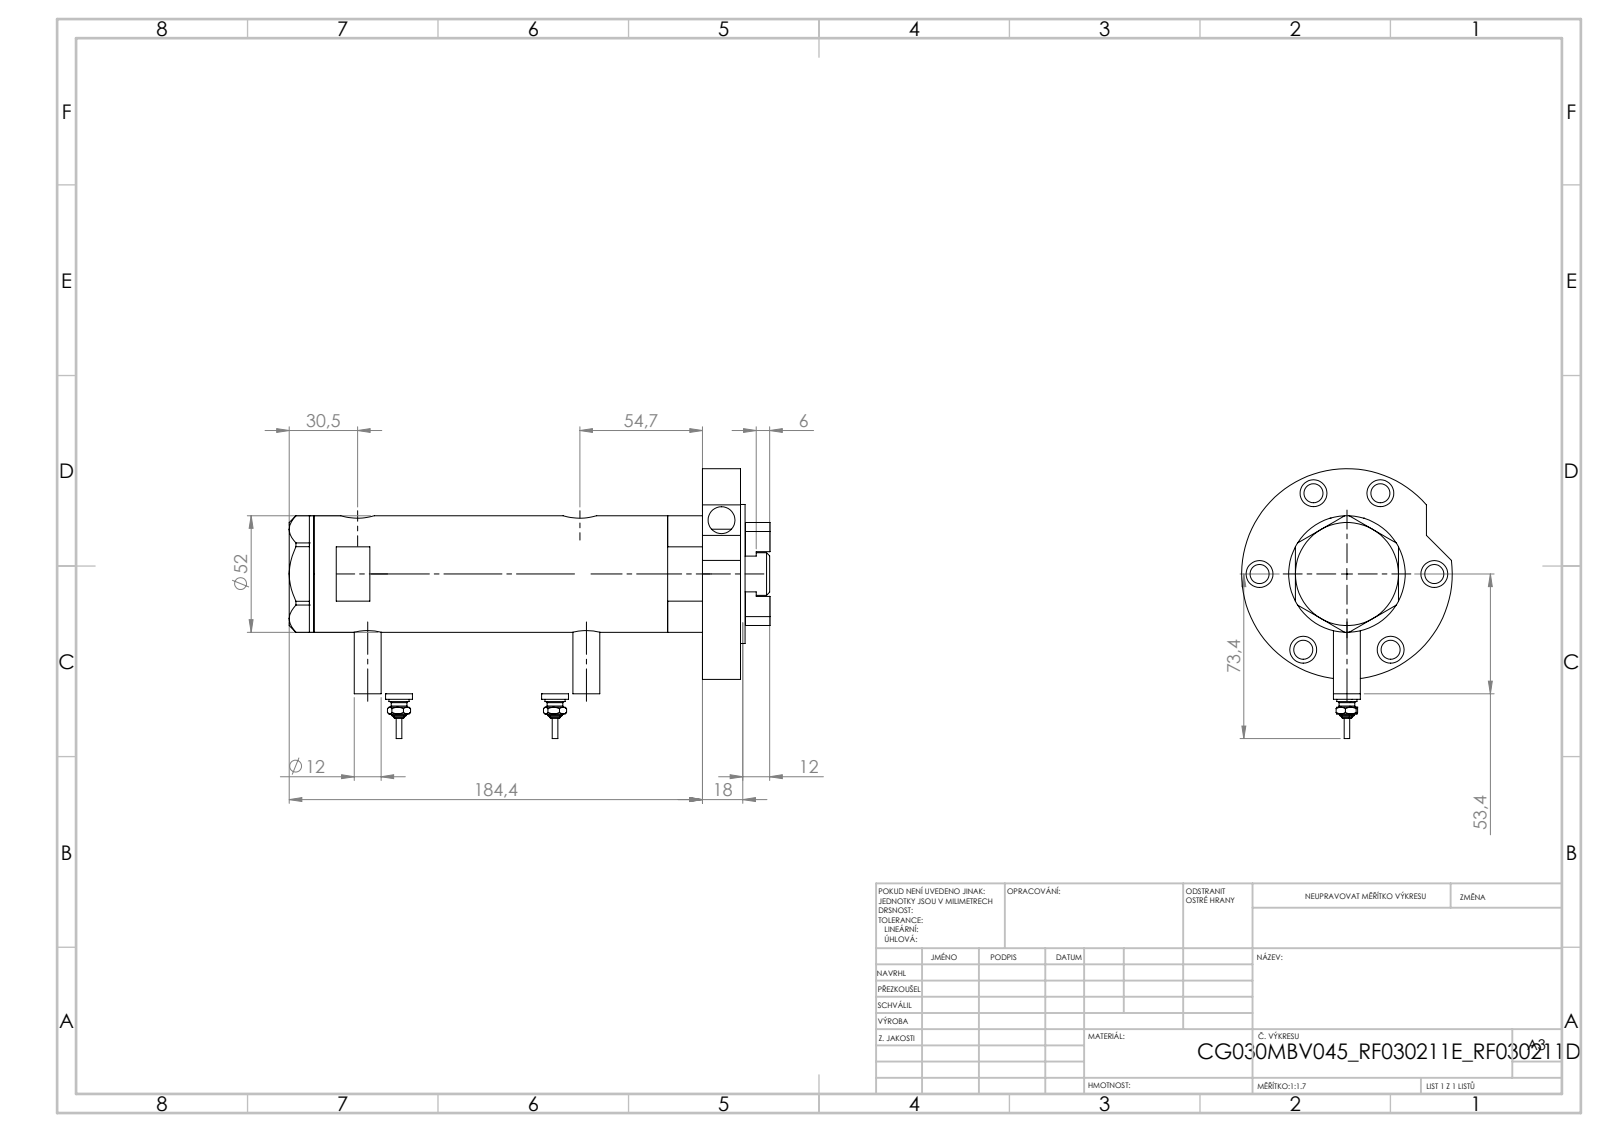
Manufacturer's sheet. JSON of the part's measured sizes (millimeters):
{"part_name": "V270CG_RF211E; V270CG_BACK; V270CG_FRONT; V270CG_RF211D (+3 more)", "step_written_by": "SolidWorks 2019 (CONFIG_CONTROL_DESIGN)", "units": "millimeters", "bodies": {"solids": 9, "faces": 330, "planar": 130, "cylindrical": 126, "other": 74}, "overall_size": [194.22, 105.3, 94], "volume_mm3": 434360, "surface_area_mm2": 108656, "round_holes": [[12, 7], [8.5, 6], [5.1, 4], [9, 4], [5, 2], [9.73, 2], [12.5, 2], [15, 2], [6.5, 1], [20, 1], [21.5, 1], [30, 1]], "round_bosses_or_shafts": [[12, 3], [9, 2], [7, 2], [4.34, 2], [2.4, 2], [94, 1], [62, 1], [52, 1]], "face_to_face_distances": [17, 150.44, 167.44, 2, 51.9, 169.44, 11, 98.54, 68.9, 70.9], "hole_center_spacings": [39, 16.74, 37.57, 46.81, 2.9, 4.5, 10, 22.37]}
